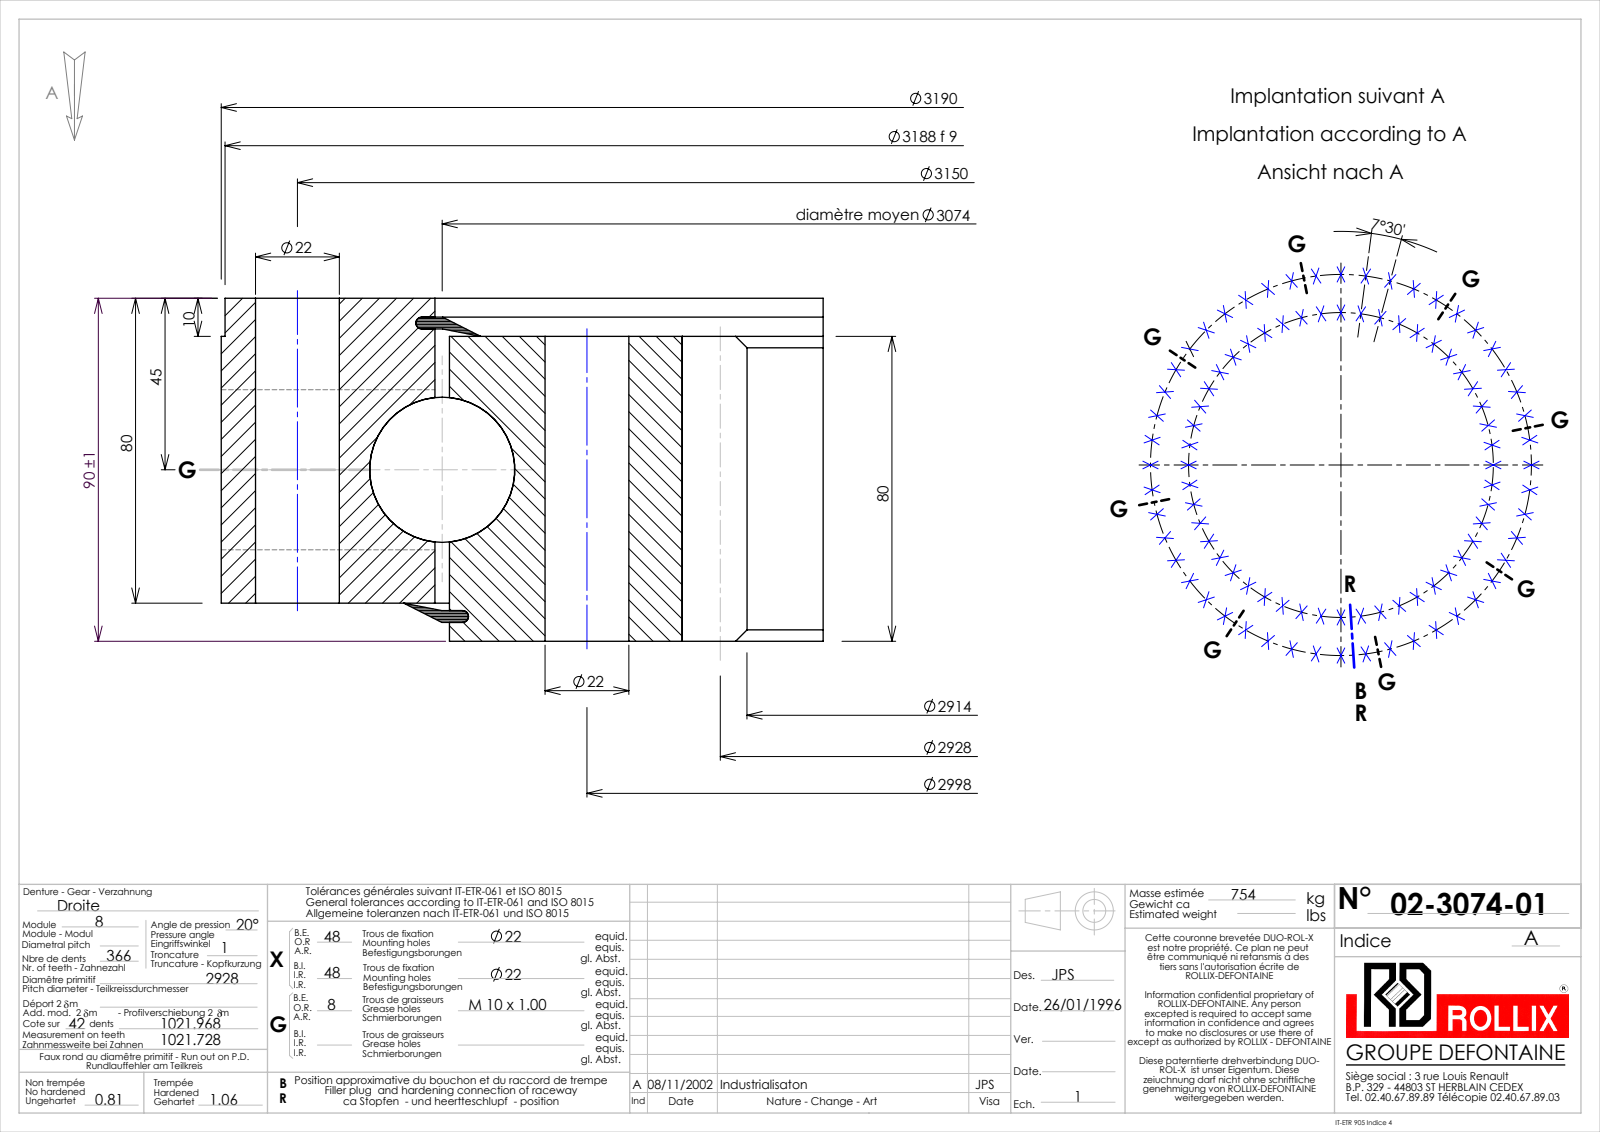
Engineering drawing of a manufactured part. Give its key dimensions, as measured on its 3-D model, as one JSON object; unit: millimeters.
{"part_name": "02-3074-01", "step_written_by": "SolidWorks 2016 (CONFIG_CONTROL_DESIGN)", "units": "millimeters", "bodies": {"solids": 5, "faces": 2462, "planar": 745, "cylindrical": 957, "other": 760}, "overall_size": [3190, 3190, 90], "volume_mm3": 84970000, "surface_area_mm2": 7897000, "round_holes": [[22, 96], [9, 8], [3077.81, 1]], "round_bosses_or_shafts": [[3190, 1], [3188, 1], [3070.19, 1]], "partial_cylinders_radius": [[1457, 1], [1474, 1]], "face_to_face_distances": [80, 10, 70, 90, 8.05, 81.95, 1.95, 71.95, 4.95, 85.05], "hole_center_spacings": [584.88, 391.32, 775.94, 1665.6, 196.08, 1325.98, 1976.72, 1147.28]}
